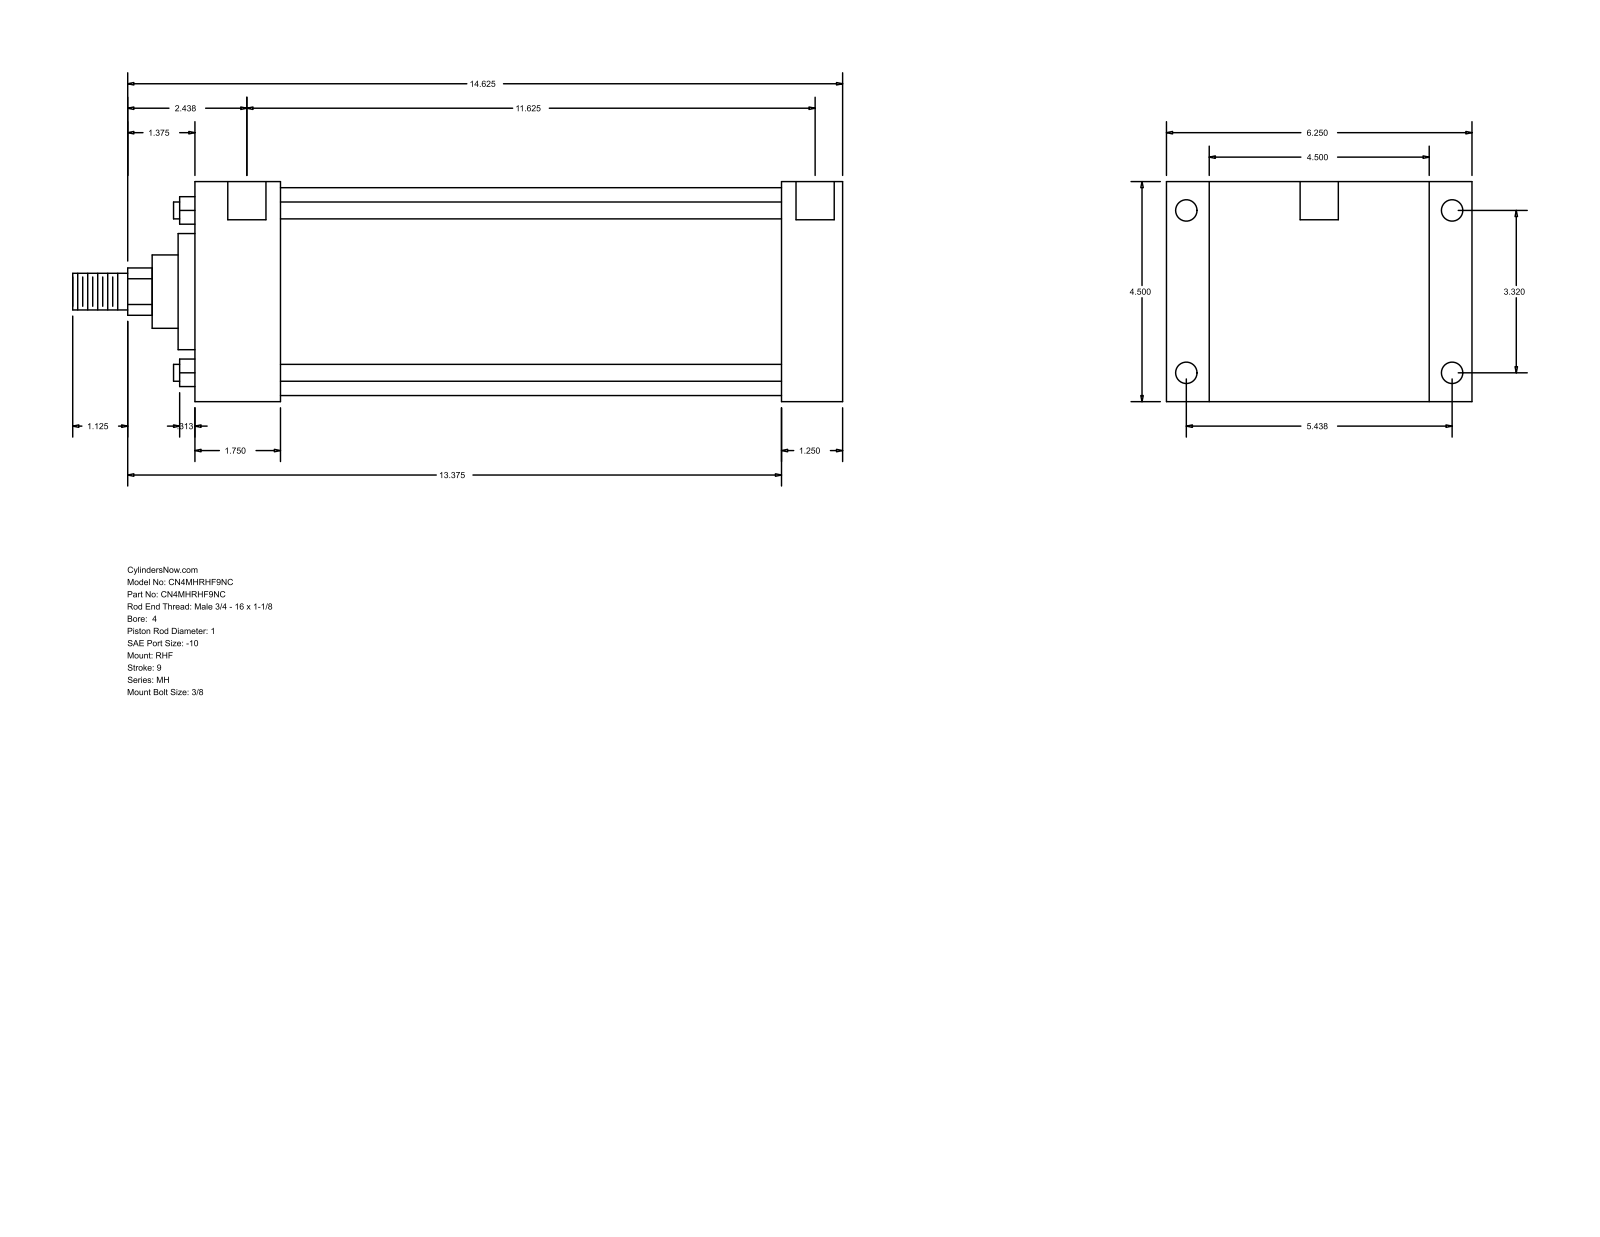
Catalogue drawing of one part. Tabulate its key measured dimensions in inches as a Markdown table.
| quantity | value |
| --- | --- |
| part name | MH_RHF__0400_1 |
| STEP written by | GSSL Pune (CONFIG_CONTROL_DESIGN) |
| units | inches |
| bodies | 0 solids, 90 faces (61 planar, 29 cylindrical, 0 other) |
| overall size | 15.75 × 6.25 × 4.5 |
| round holes (diameter × count) | 0.344 × 4, 0.438 × 4, 0.781 × 2 |
| round bosses / shafts (diameter × count) | 0.345 × 4, 4.25 × 1, 2.375 × 1, 1.5 × 1, 1 × 1, 0.75 × 1 |
| partial cylindrical surfaces (radius × count) | 0.484 × 1 |
| main face-to-face distances | 4.5, 13.25, 12, 1.25, 0.875, 5.375, 1.75, 10.25, 11.5, 6.25 |
| hole center spacings | 0.062, 3.32, 5.438, 6.371, 11.687, 11.75, 11.625 |
